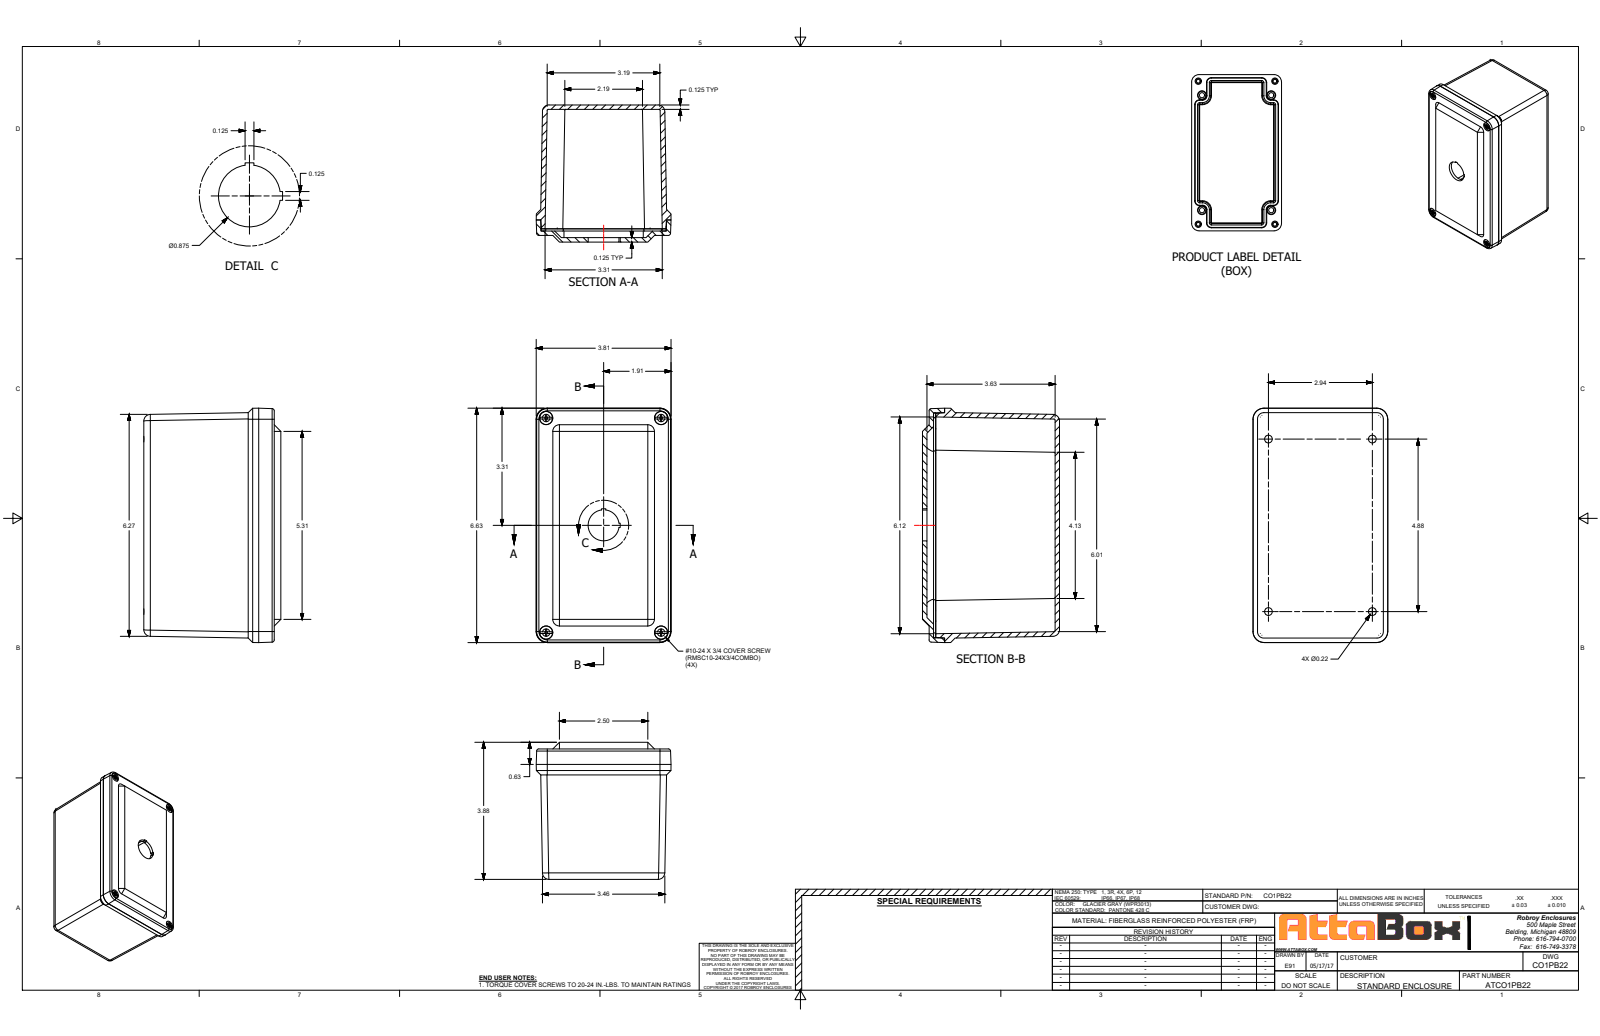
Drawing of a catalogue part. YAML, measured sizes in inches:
part_name: "CO1PB22"
step_written_by: "SolidWorks 2018 (AUTOMOTIVE_DESIGN)"
units: inches
bodies: {solids: 11, faces: 387, planar: 189, cylindrical: 102, other: 96}
overall_size: [6.625, 3.875, 3.812]
volume: 20.27
surface_area: 266.9
round_holes:
  - {diameter: 0.219, count: 8}
  - {diameter: 0.159, count: 4}
  - {diameter: 0.19, count: 4}
  - {diameter: 0.375, count: 4}
round_bosses_or_shafts:
  - {diameter: 0.371, count: 4}
  - {diameter: 0.27, count: 4}
  - {diameter: 0.177, count: 4}
partial_cylinders:
  - {radius: 0.031, count: 20}
  - {radius: 0.012, count: 16}
  - {radius: 0.176, count: 4}
  - {radius: 0.22, count: 4}
  - {radius: 0.313, count: 4}
  - {radius: 0.325, count: 4}
  - {radius: 0.062, count: 2}
  - {radius: 0.063, count: 2}
face_to_face_distances: [0.125, 0.131, 3.75, 0.187, 3.563, 0.5, 3.875, 3.625, 0.063, 3.438]
hole_center_spacings: [0.614, 3.15, 5.471, 6.283, 2.938, 3.25, 4.875, 5.692]
